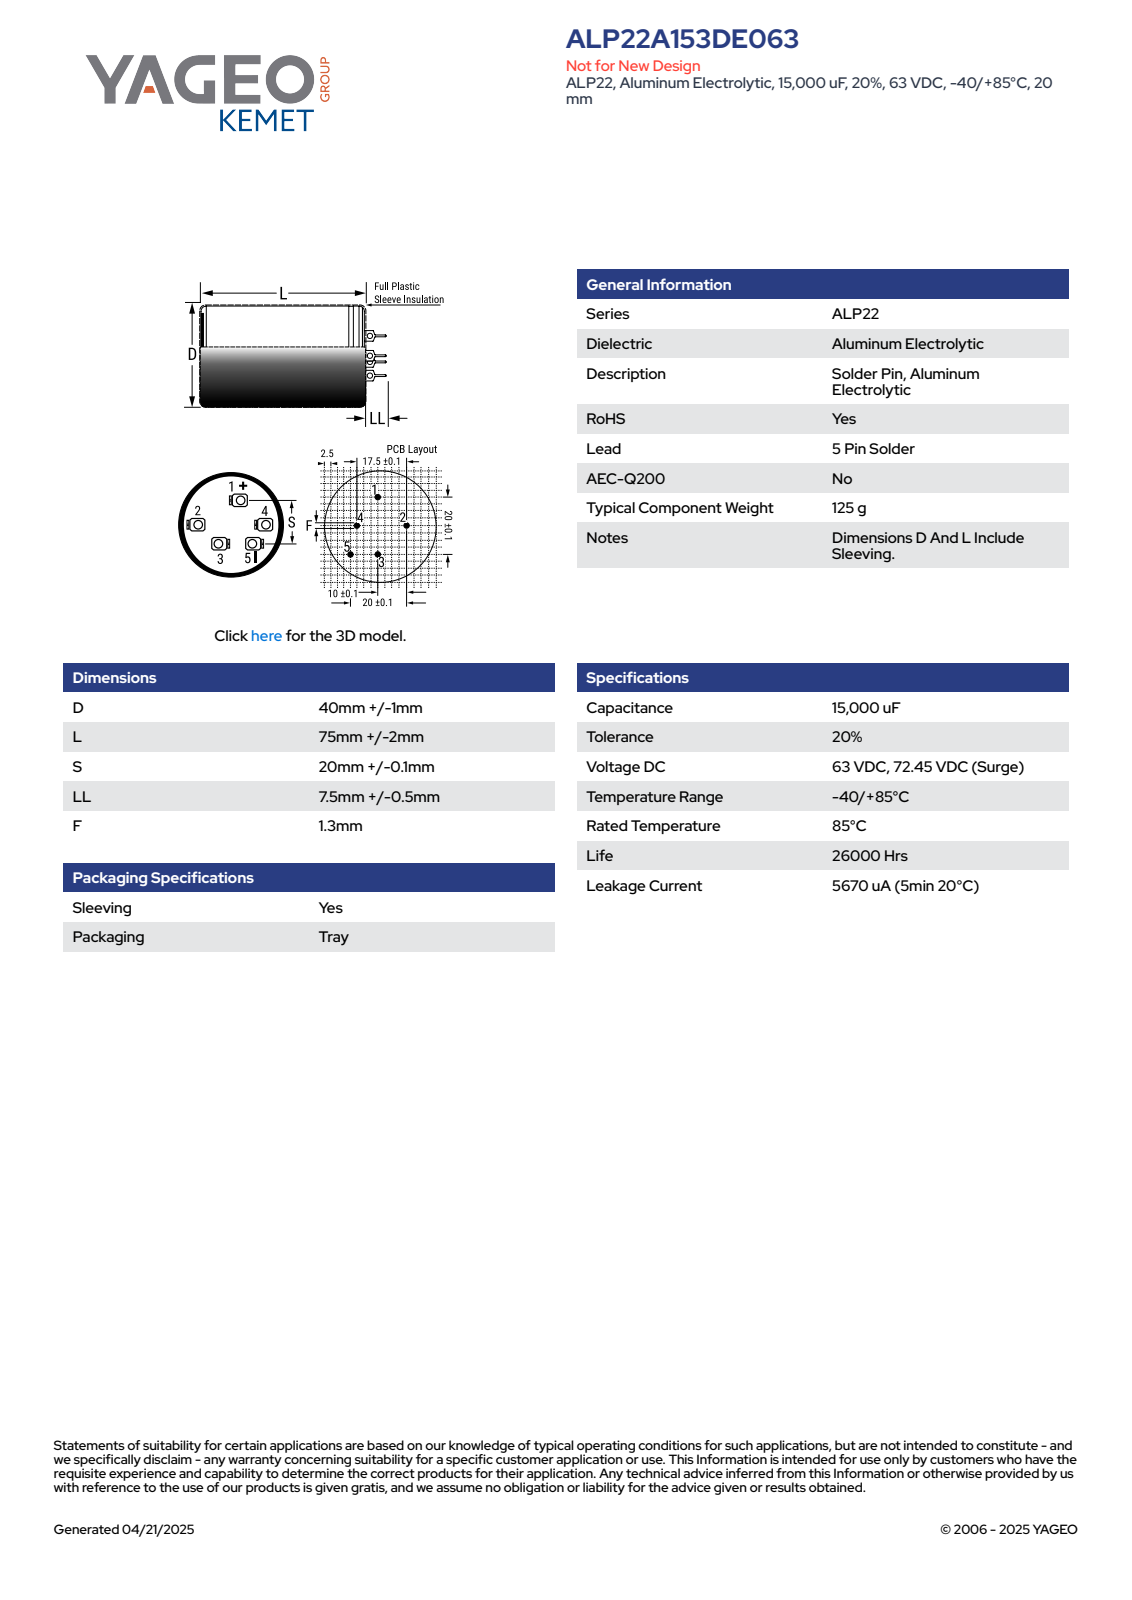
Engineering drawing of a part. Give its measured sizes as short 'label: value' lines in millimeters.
name: CARS5_D41L77LL7.5S20F1.3; Terminal_Rivet; Terminal_SolderTag7.5; Can5_2
written by: SolidWorks 2014 (AUTOMOTIVE_DESIGN)
unit: mm
bodies: 11 solids, 269 faces (135 planar, 72 cylindrical, 62 other)
size: 84.5 × 41 × 41
volume: 101 360 mm³; area: 12 919 mm²
holes: 5× ⌀1.3, 3× ⌀1
bosses: 5× ⌀3, 1× ⌀41
rounds: 3× R0.32, 1× R20.49
face distances: 77, 77.25, 10, 9.75, 7.5, 17.5, 0.45, 0.7, 77.7, 2.25
hole spacings: 10, 10.08, 11.79, 12.5, 14.14, 15.05, 17.5, 19.08
